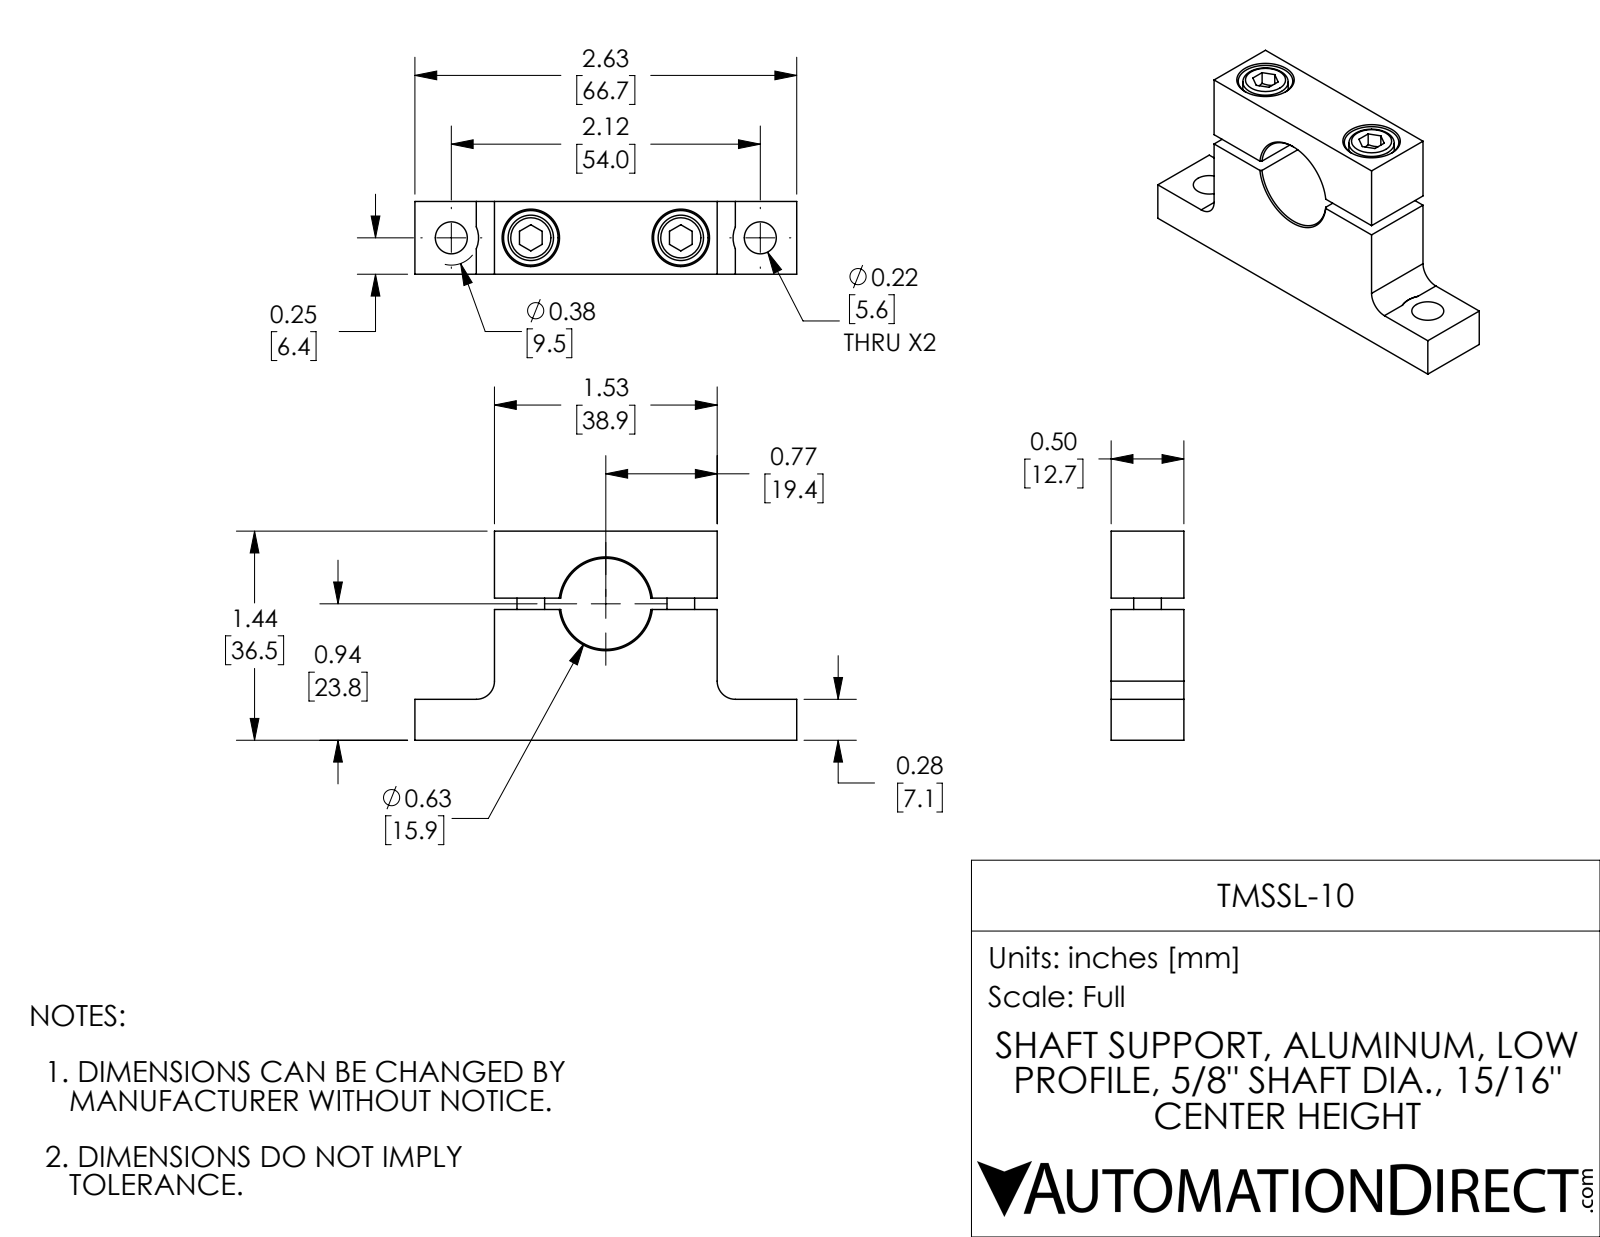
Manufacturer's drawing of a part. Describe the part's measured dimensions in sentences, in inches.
The part is named "TMSSL-10". Its 3-D file was written by "SolidWorks 2017 (AUTOMOTIVE_DESIGN)". It is 4 solids with 95 faces: 38 planar, 31 cylindrical and 26 other. Overall it measures 2.625 by 1.437 by 0.5 inches. Its volume is 1.024 cubic inches and its surface area 13.28 square inches. Round holes: 2 of diameter 0.145, 2 of diameter 0.201, 2 of diameter 0.22, 2 of diameter 0.375, 1 of diameter 0.625. Round bosses or shafts: 2 of diameter 0.312, 2 of diameter 0.19. Partial cylindrical surfaces (rounded edges, fillets, slot ends): 2 of radius 0.125, 1 of radius 0.187, 1 of radius 0.188. The main face-to-face distances are 0.5, 1.437, 1.531, 0.898, 0.539, 0.976, 0.078, 0.461, 0.281, 0.617. The hole center spacings are 0.546, 1.578, 1.031, 2.124.
